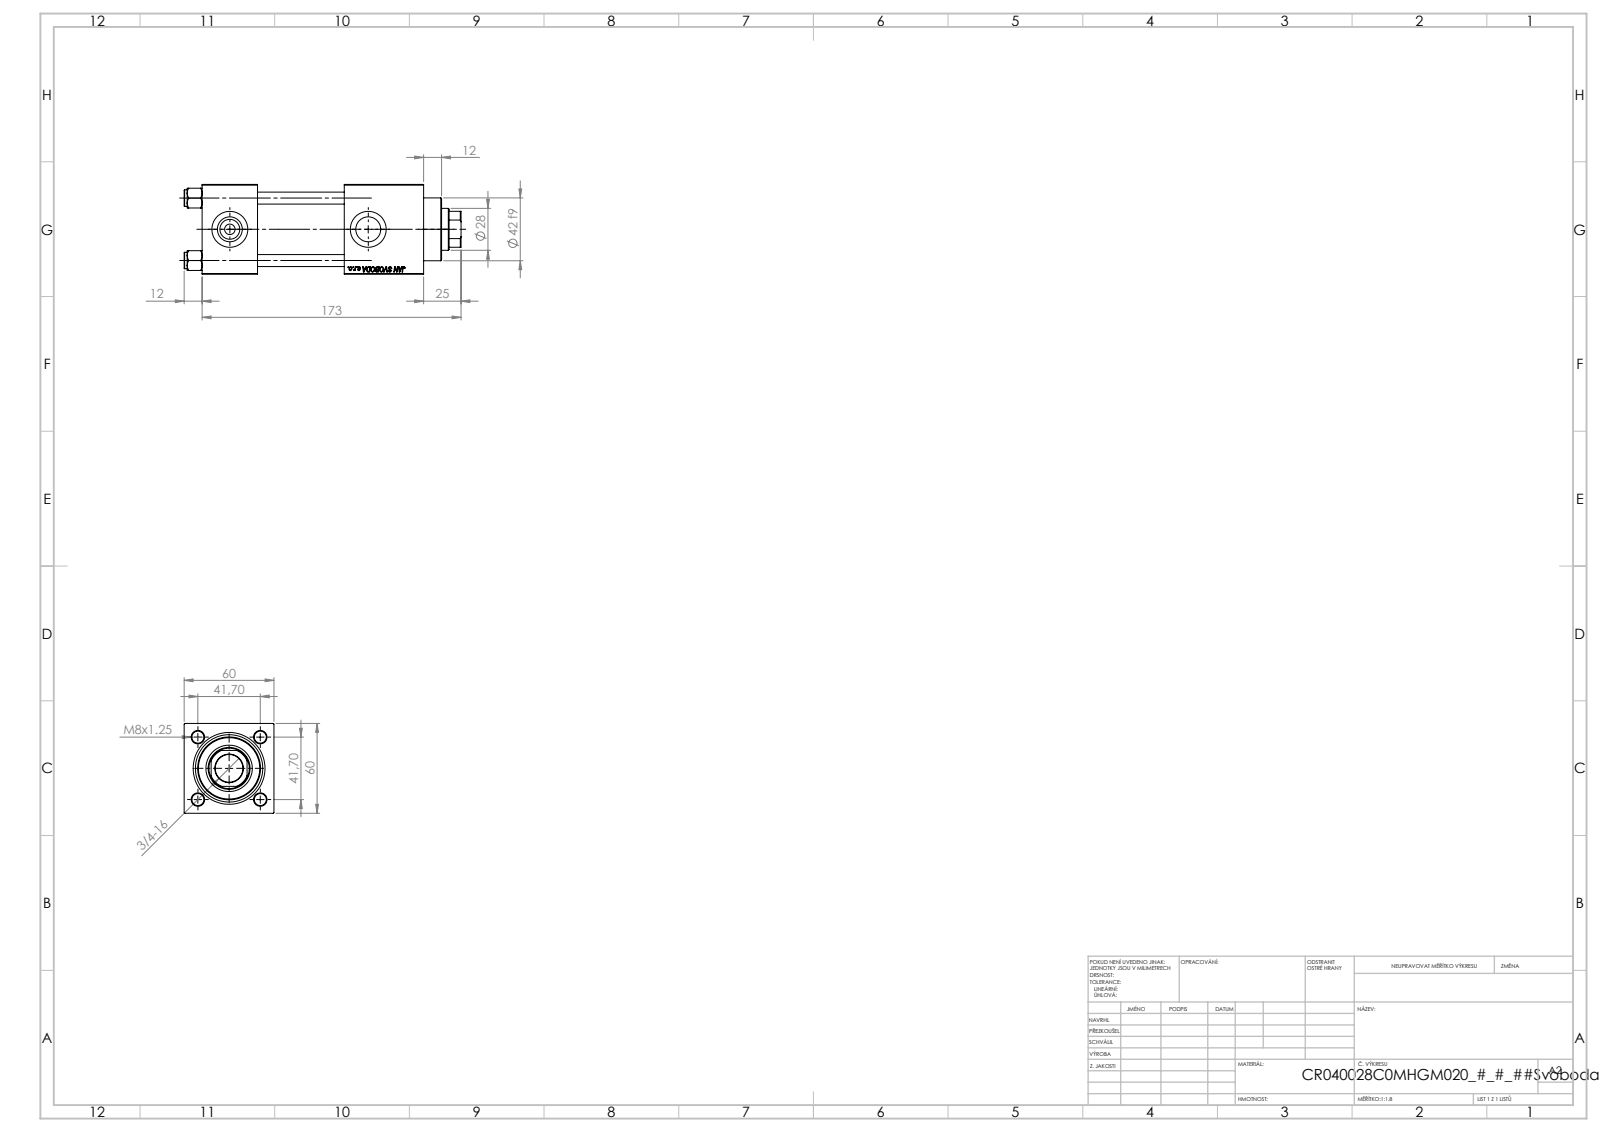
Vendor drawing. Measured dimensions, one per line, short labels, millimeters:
name: NUT_M5_C; V215CR_C_Body; V215_VC_A; V215CR_C_TYCINKA (+1 more)
written by: SolidWorks 2019 (CONFIG_CONTROL_DESIGN)
unit: mm
bodies: 11 solids, 1148 faces (526 planar, 86 cylindrical, 536 other)
size: 185 × 60 × 60
volume: 424 183 mm³; area: 111 432 mm²
holes: 4× ⌀8, 2× ⌀7, 2× ⌀16.66, 2× ⌀24, 1× ⌀18.5, 1× ⌀28, 1× ⌀31, 1× ⌀40, 1× ⌀45
bosses: 4× ⌀11, 1× ⌀46, 1× ⌀42
rounds: 1× R13.5
face distances: 60, 37, 58, 95, 53, 119.3, 82.3, 24.3, 148, 111
hole spacings: 29.49, 41.7, 58.97, 92.5
